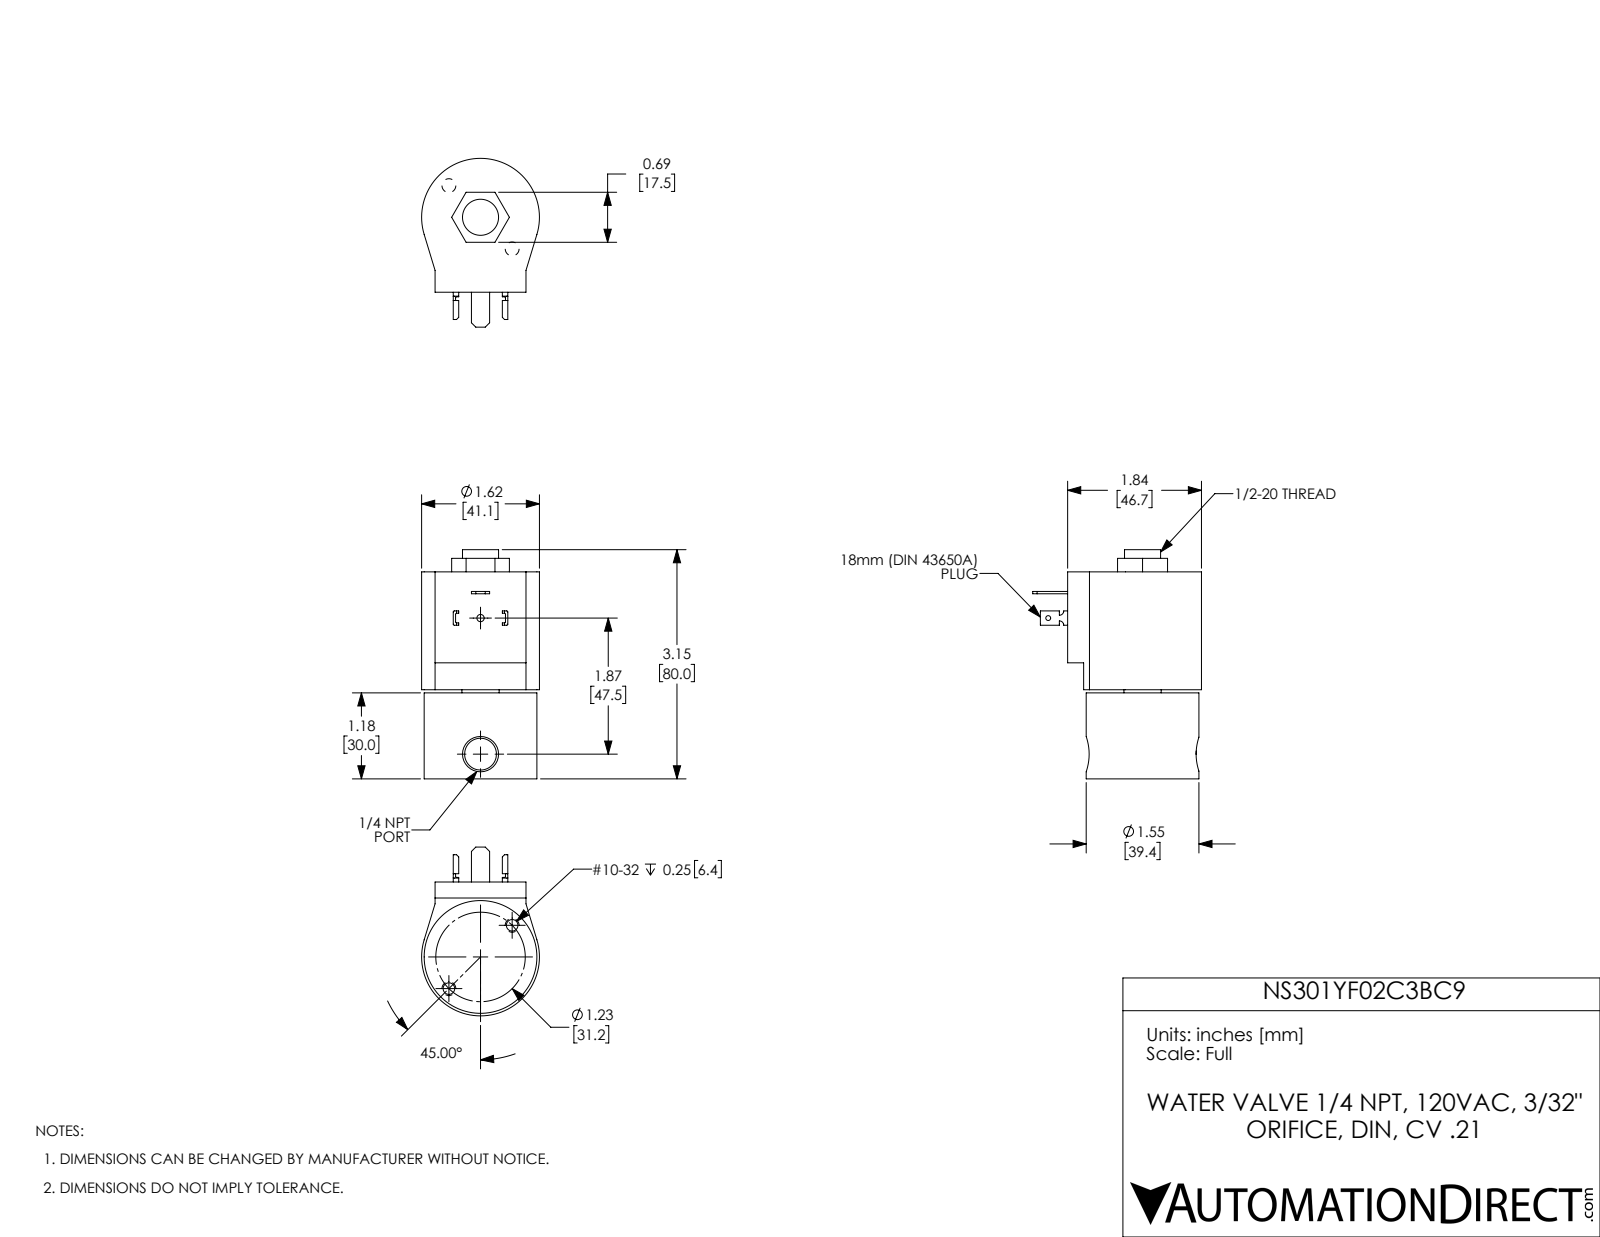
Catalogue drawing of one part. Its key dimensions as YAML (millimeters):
part_name: "NS301YF02C3BC9"
step_written_by: "SolidWorks 2017 (AUTOMOTIVE_DESIGN)"
units: millimeters
bodies: {solids: 6, faces: 130, planar: 73, cylindrical: 49, other: 8}
overall_size: [80, 58.9, 41.1]
volume: 98760
surface_area: 21340
round_holes:
  - {diameter: 4, count: 2}
  - {diameter: 1.7, count: 1}
  - {diameter: 2.5, count: 1}
  - {diameter: 11.1, count: 1}
  - {diameter: 12.6, count: 1}
  - {diameter: 13, count: 1}
  - {diameter: 29.3, count: 1}
round_bosses_or_shafts:
  - {diameter: 39.4, count: 1}
partial_cylinders:
  - {radius: 0.4, count: 8}
  - {radius: 1.5, count: 2}
  - {radius: 20.6, count: 1}
face_to_face_distances: [72.3, 30, 42.2, 31.1, 1.1, 41.1, 32.7, 2.7, 1.6, 39.6]
hole_center_spacings: [15.6, 31.2, 47.5]
